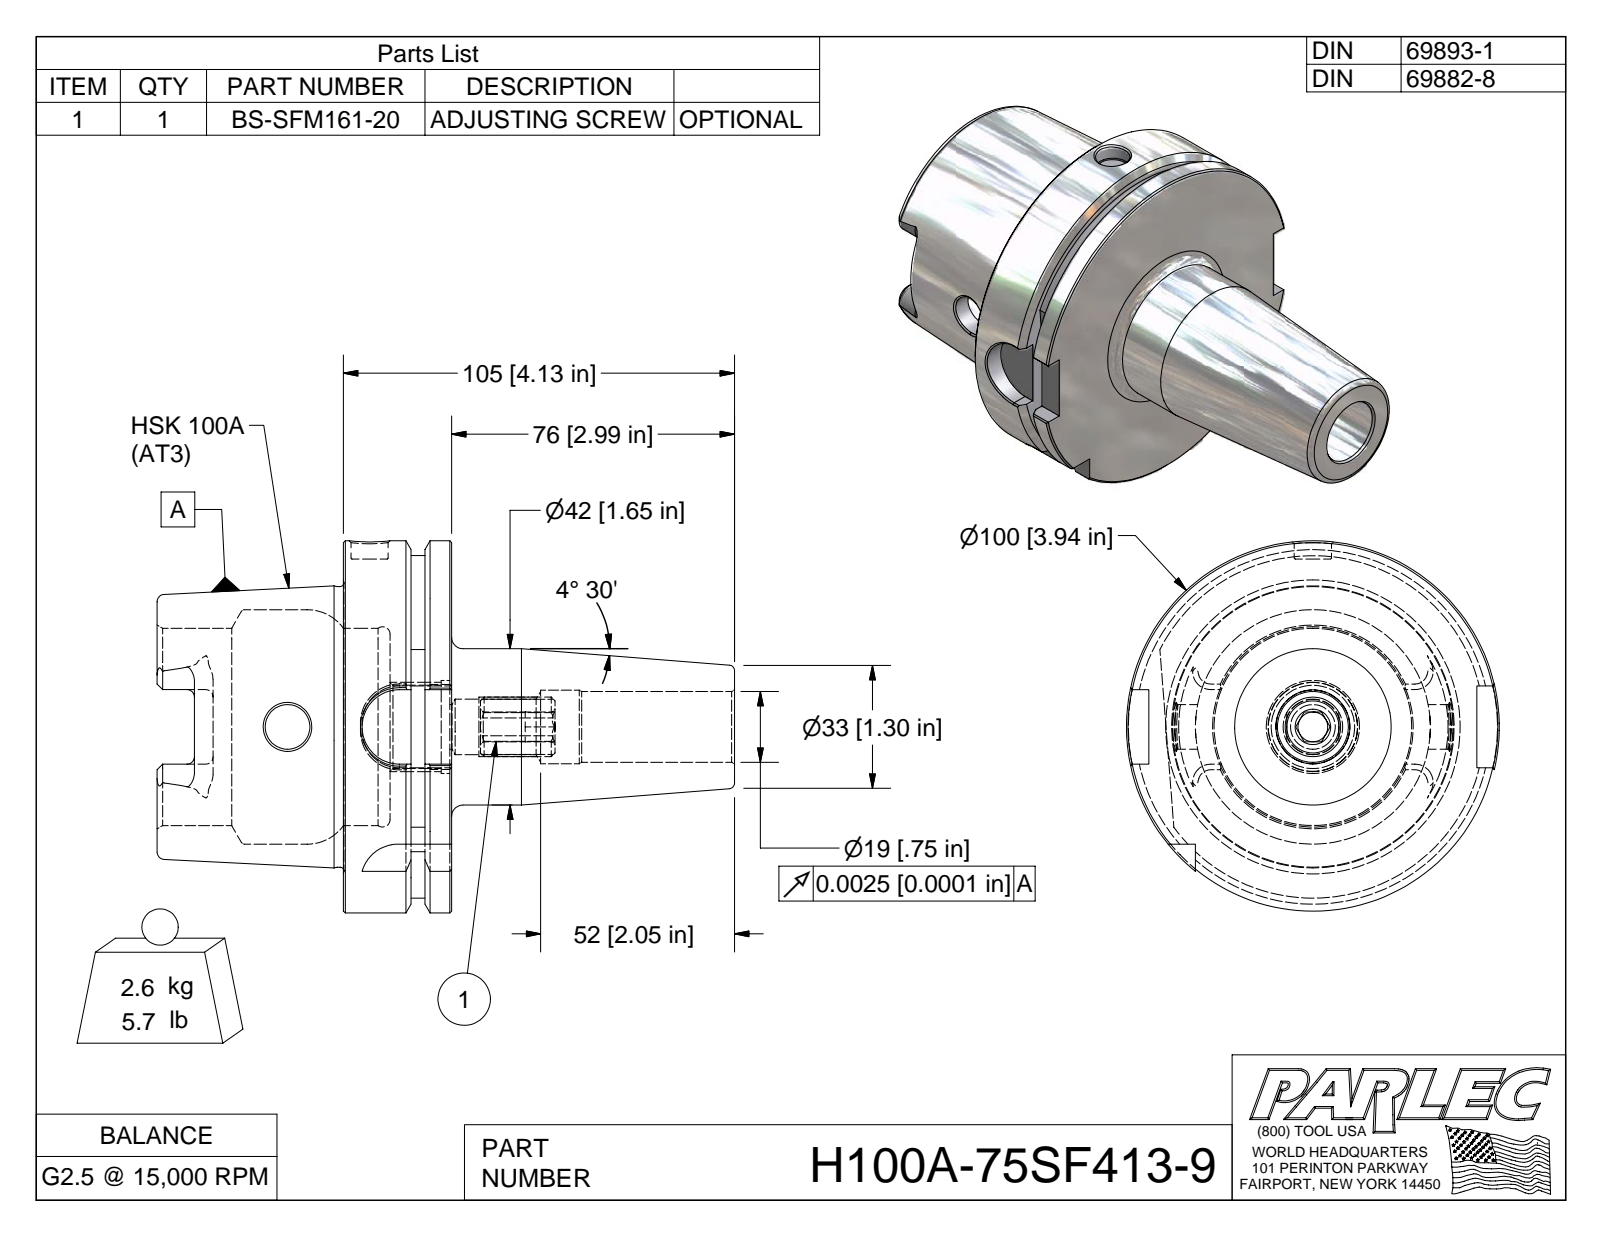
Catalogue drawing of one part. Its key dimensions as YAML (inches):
part_name: "H100A-75SF413-9; H100A-75SF413-9-1; BS-SFM161-20"
step_written_by: "Autodesk Inventor 2009 (AUTOMOTIVE_DESIGN)"
units: inches
bodies: {solids: 2, faces: 149, planar: 49, cylindrical: 30, other: 70}
overall_size: [6.099, 3.937, 3.937]
volume: 19.94
surface_area: 99.6
round_holes:
  - {diameter: 0.394, count: 1}
  - {diameter: 0.472, count: 1}
  - {diameter: 0.749, count: 1}
  - {diameter: 0.779, count: 1}
  - {diameter: 0.881, count: 1}
  - {diameter: 0.985, count: 1}
  - {diameter: 2.087, count: 1}
  - {diameter: 2.48, count: 1}
round_bosses_or_shafts:
  - {diameter: 3.937, count: 1}
  - {diameter: 2.967, count: 1}
  - {diameter: 1.654, count: 1}
partial_cylinders:
  - {radius: 0.394, count: 4}
  - {radius: 0.079, count: 3}
  - {radius: 0.192, count: 2}
  - {radius: 0.315, count: 1}
  - {radius: 1.811, count: 1}
face_to_face_distances: [1.142, 0.492, 0.65, 1.969, 2.461, 3.11, 2.682, 0.713, 0.221, 0.428]
